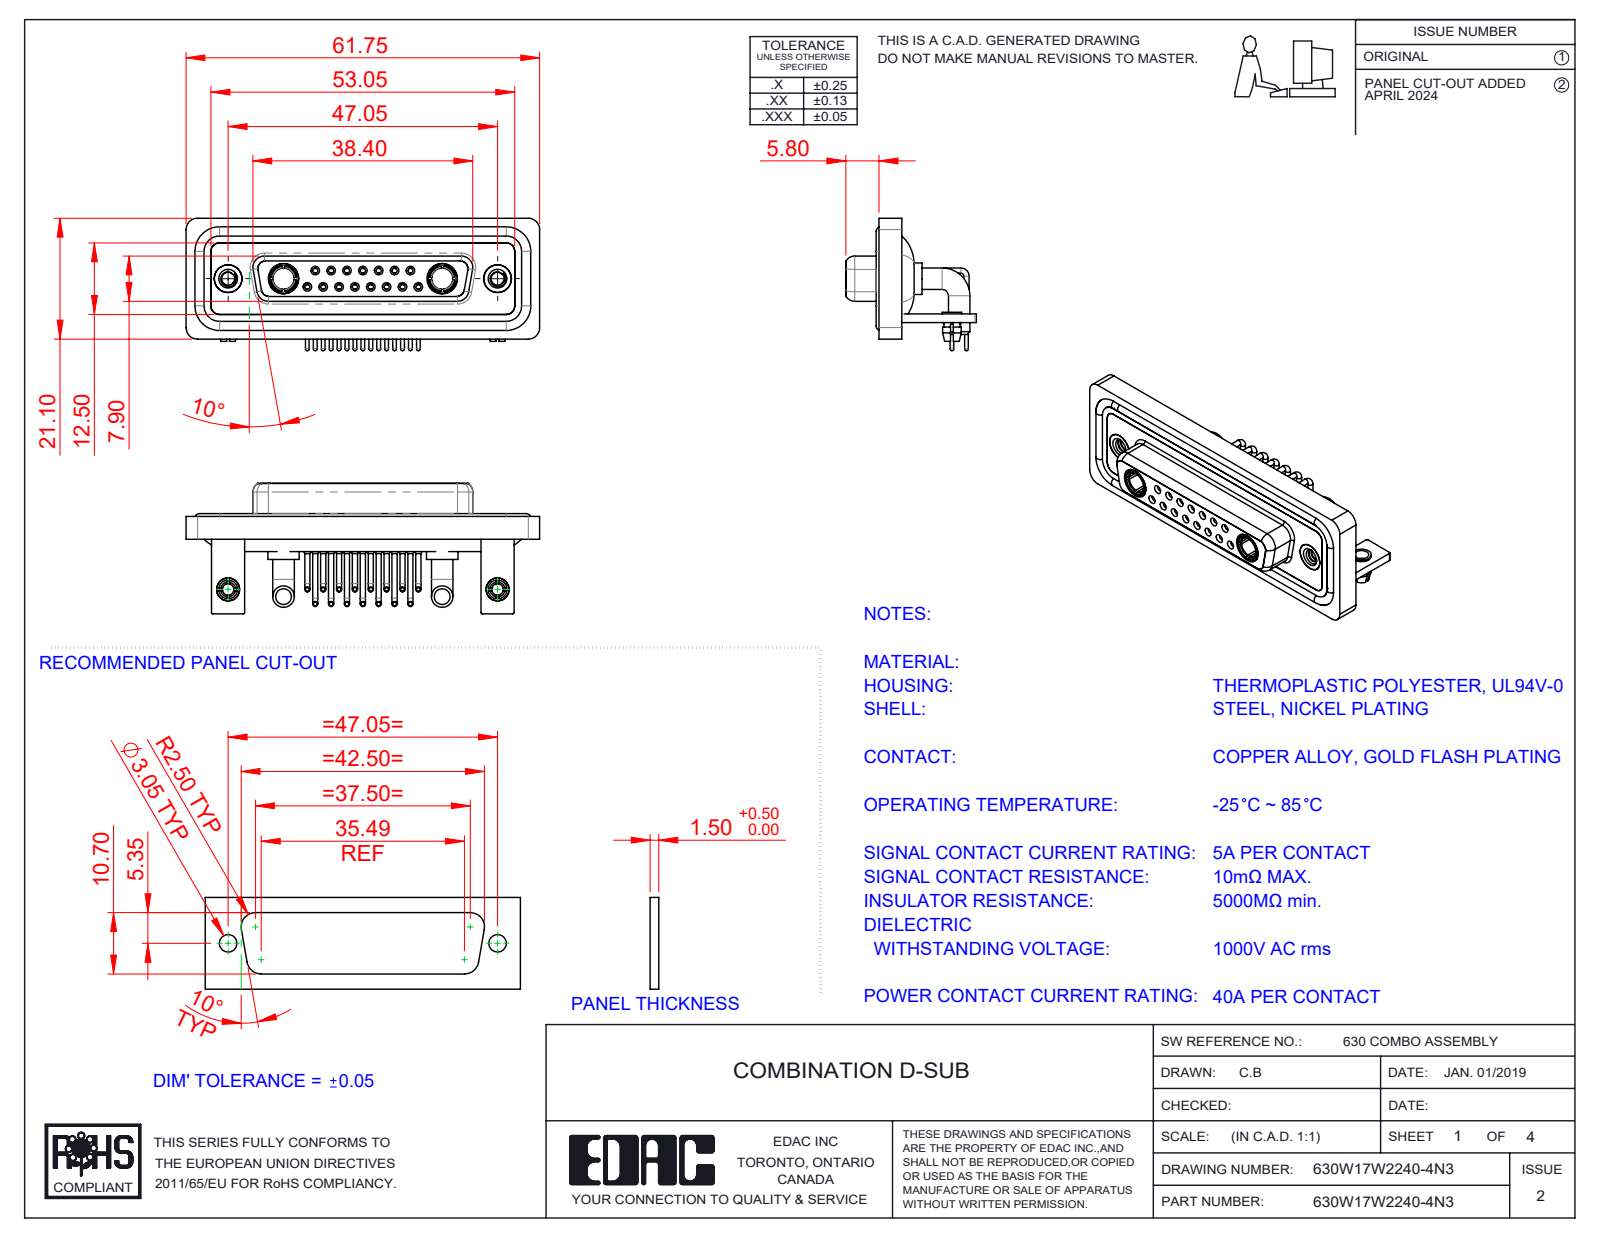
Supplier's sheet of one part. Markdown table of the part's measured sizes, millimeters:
| quantity | value |
| --- | --- |
| part name | 630Combo Waterproof Housing_25 Contacts; 630W17W2140-4N3; 630Combo Stabilizer Bracket_50 Contacts; 630Combo Board Lock_50 Contacts (+7 more) |
| STEP written by | SolidWorks 2023 (CONFIG_CONTROL_DESIGN) |
| units | millimeters |
| bodies | 30 solids, 1477 faces (456 planar, 639 cylindrical, 382 other) |
| overall size | 61.75 × 23.12 × 22.8 |
| volume | 9 035 mm³ |
| surface area | 15 564 mm² |
| round holes (diameter × count) | 2 × 17, 0.9 × 15, 1.1 × 15, 1.5 × 15, 1.6 × 8, 1.7 × 7, 4.85 × 4, 2.26 × 2, 2.5 × 2, 3.2 × 2, 3.7 × 2, 4 × 2 |
| round bosses / shafts (diameter × count) | 0.9 × 15, 0.65 × 15, 1.6 × 11, 3.75 × 4, 5.5 × 2, 5.2 × 2, 4.96 × 2, 4.95 × 2 |
| partial cylindrical surfaces (radius × count) | 2 × 19, 1.5 × 18, 0.25 × 16, 1.35 × 8, 1.6 × 8, 0.5 × 5, 0.6 × 4, 0.65 × 4 |
| main face-to-face distances | 0.4, 1.8, 2.9, 3.7, 1.5, 4.1, 1.1, 1.4, 1.6, 3.1 |
| hole center spacings | 3.16, 2.77, 5.54, 8.31, 5.04, 7.49, 11.08, 5.03 |
